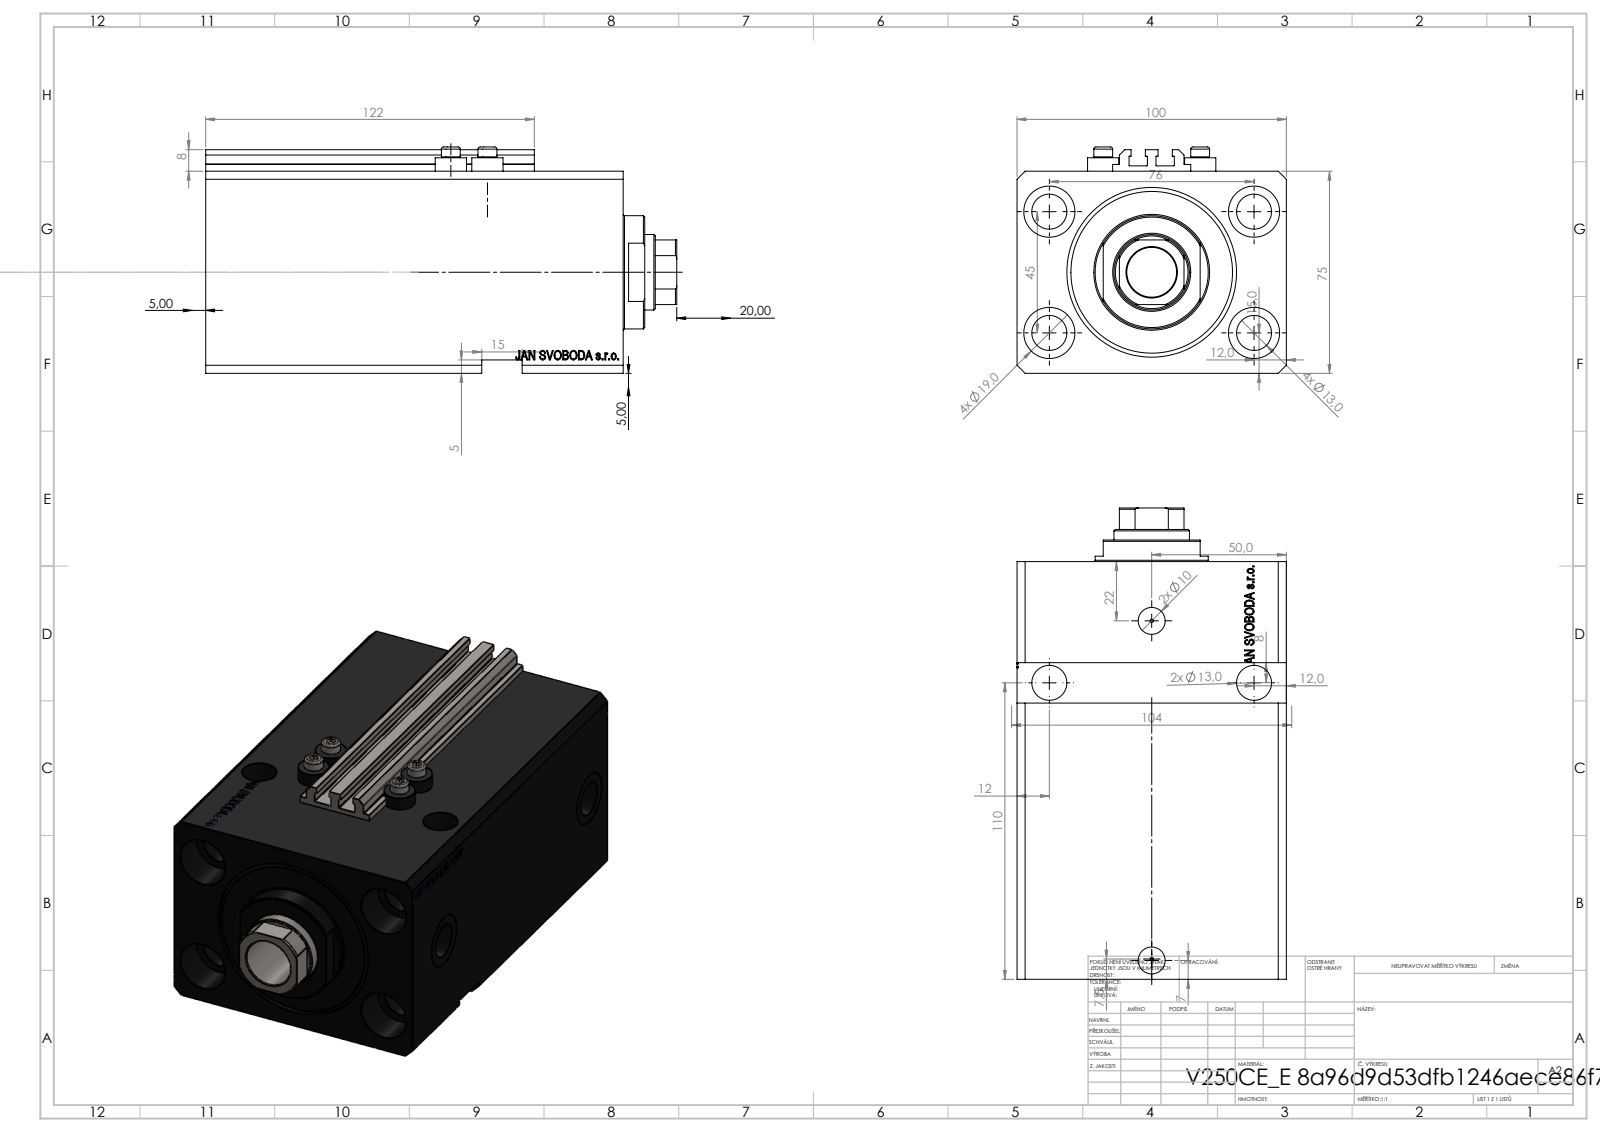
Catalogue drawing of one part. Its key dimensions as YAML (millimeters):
part_name: "ALLEN BOLT V250CE; V250CE_E_Body; V250CE_C_VCP; V250CE_VC_E"
step_written_by: "SolidWorks 2019 (CONFIG_CONTROL_DESIGN)"
units: millimeters
bodies: {solids: 8, faces: 1108, planar: 535, cylindrical: 146, other: 427}
overall_size: [175, 100, 84]
volume: 940698
surface_area: 175915
round_holes:
  - {diameter: 13, count: 8}
  - {diameter: 1.25, count: 4}
  - {diameter: 4, count: 4}
  - {diameter: 19, count: 4}
  - {diameter: 10, count: 2}
  - {diameter: 13.16, count: 2}
  - {diameter: 20, count: 2}
  - {diameter: 18.5, count: 1}
  - {diameter: 28, count: 1}
  - {diameter: 50, count: 1}
  - {diameter: 63, count: 1}
round_bosses_or_shafts:
  - {diameter: 11.6, count: 4}
  - {diameter: 7, count: 4}
  - {diameter: 42, count: 1}
partial_cylinders:
  - {radius: 0.2, count: 10}
  - {radius: 13.5, count: 1}
face_to_face_distances: [75, 100, 155, 20, 11.9, 143.1, 135, 123.1, 8, 80]
hole_center_spacings: [44.16, 76, 13.6, 20.72, 27.59, 33.62, 36, 38.48]
